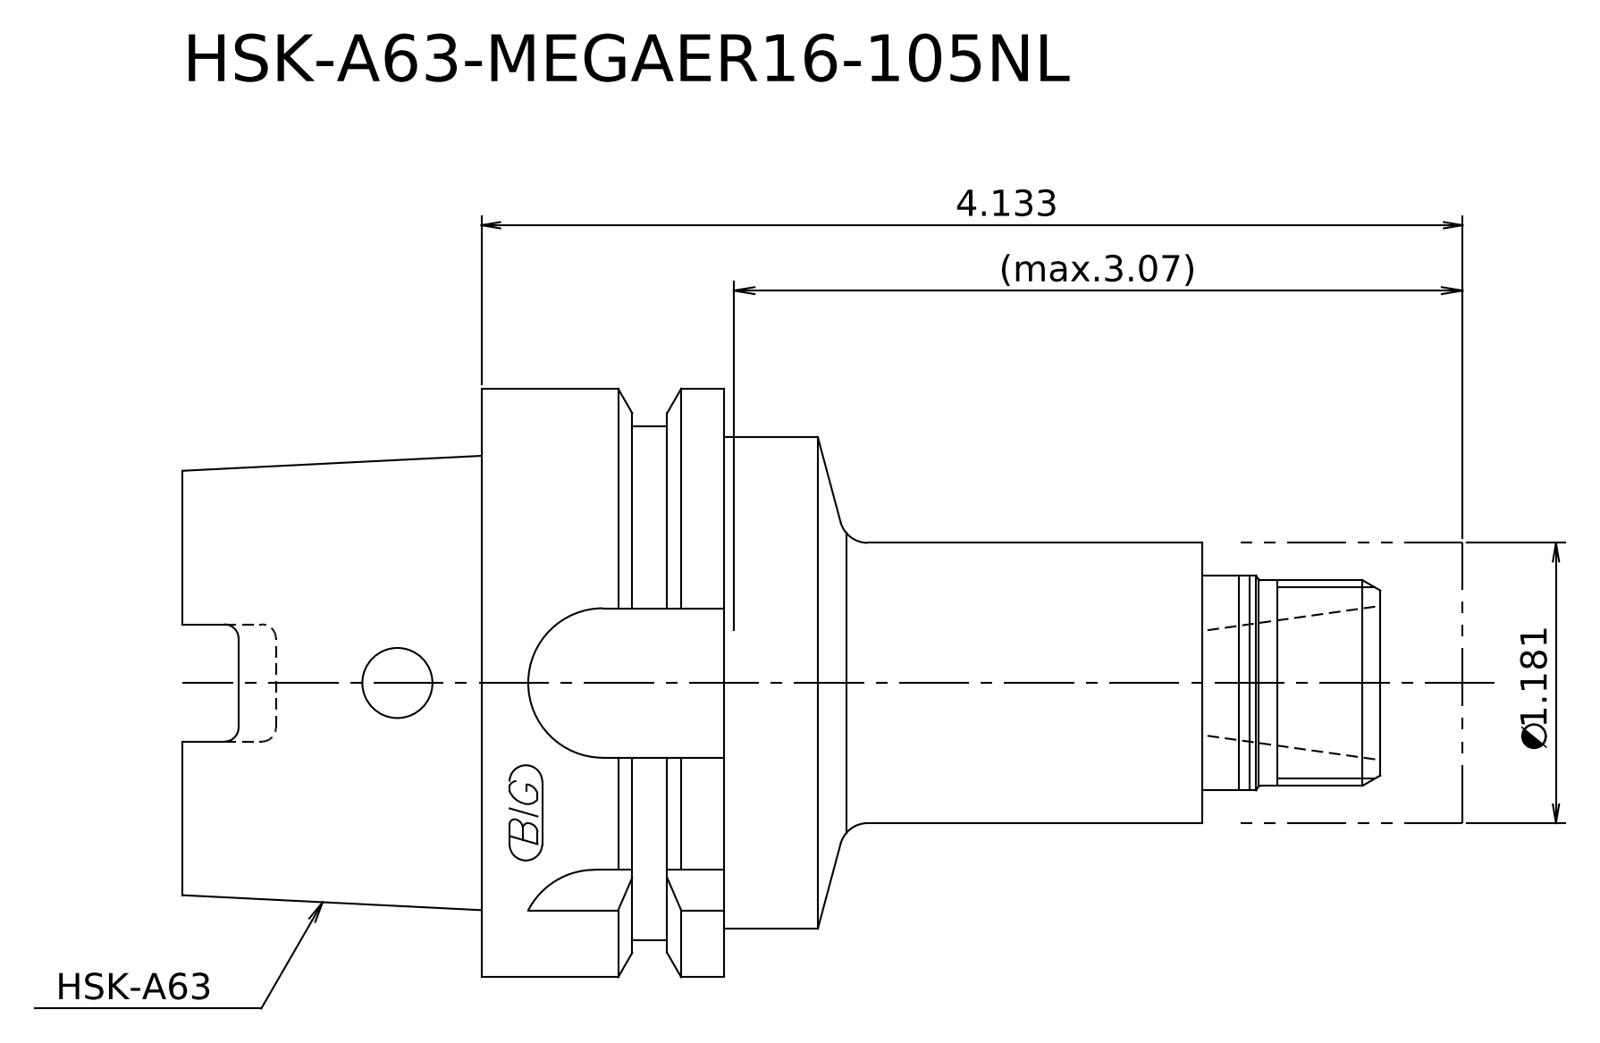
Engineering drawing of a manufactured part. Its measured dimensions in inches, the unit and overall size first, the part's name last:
Units: inches
Overall size (bounding box): 5.394 × 2.48 × 2.48
Round bosses / shafts (diameter × count): ⌀2.48 ×1, ⌀2.165 ×1, ⌀2.071 ×1, ⌀1.181 ×1, ⌀0.906 ×1, ⌀0.866 ×1
Main face-to-face distances: 1.26, 1.024, 2.283, 2.126, 3.15, 4.409, 0.984, 3.11, 4.134, 5.394
Volume: 12.97 in³ · Surface area: 41.9 in²
Bodies: 2 solids, 23 faces (9 planar, 8 cylindrical, 6 other)
STEP written by: Kubotek KeyCreator 2011 V10.0.2 (22737) (automotive_design)
